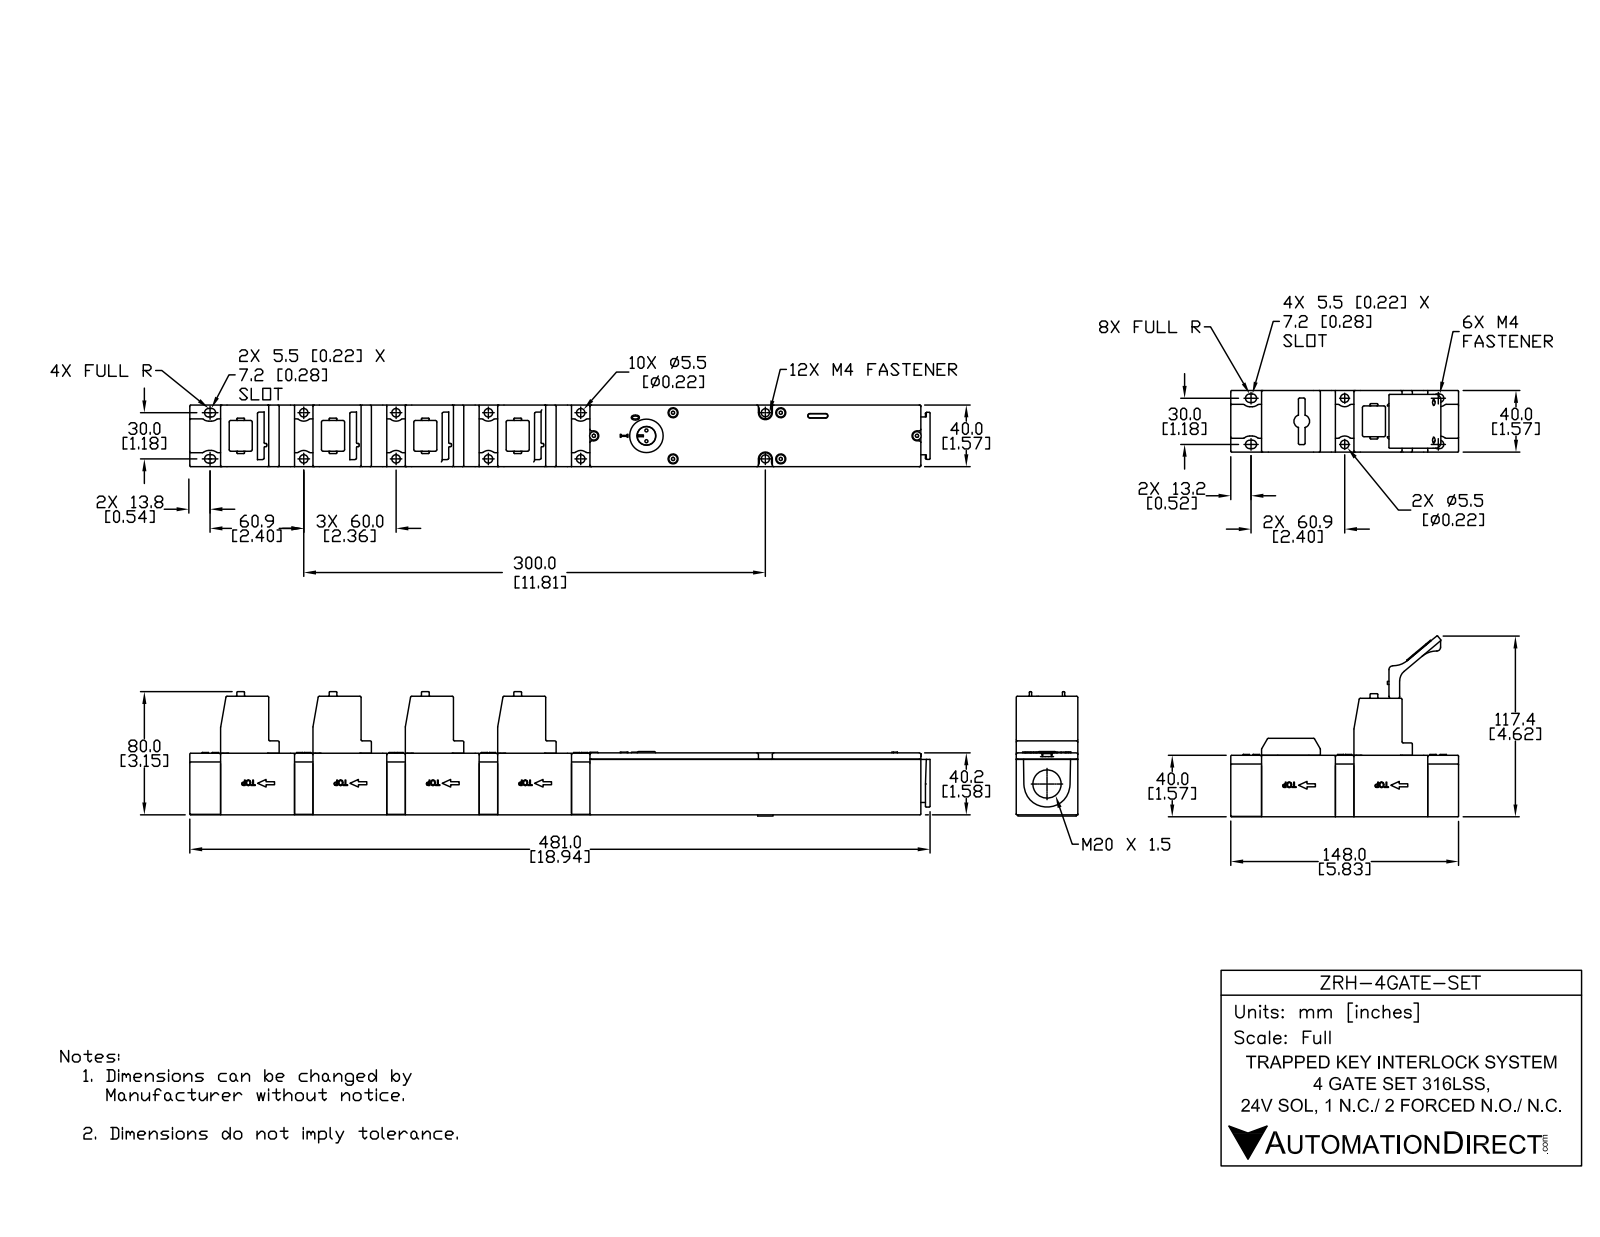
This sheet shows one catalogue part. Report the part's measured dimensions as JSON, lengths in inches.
{"part_name": "ST2323_STS-Schluessel_mit_Kodierung_NEU; ST2110_B; ST2130_01; ST2330_Bajonett (+4 more)", "step_written_by": "SolidWorks 2017 (AUTOMOTIVE_DESIGN)", "units": "inches", "bodies": {"solids": 44, "faces": 17763, "planar": 7815, "cylindrical": 2190, "other": 7758}, "overall_size": [19.525, 18.937, 4.641], "volume_in3": 127.8, "surface_area_in2": 595, "round_holes": [[0.157, 24], [0.217, 16], [0.097, 12], [0.079, 10], [0.13, 6], [0.097, 4], [0.256, 4], [0.236, 3], [0.209, 2], [0.079, 1], [0.134, 1], [0.374, 1]], "round_bosses_or_shafts": [[0.217, 6], [0.118, 6], [0.394, 5], [0.472, 1], [0.276, 1], [0.228, 1], [0.161, 1]], "partial_cylinders_radius": [[0.02, 654], [0.039, 267], [0.03, 207], [0.018, 114], [0.217, 52], [0.006, 46], [0.079, 37], [0.108, 36]], "face_to_face_distances": [1.575, 2.362, 1.89, 0.472, 4.252, 4.724, 13.11, 8.386, 10.748, 8.656], "hole_center_spacings": [2.362, 1.181, 0.571, 2.641, 8.656, 4.363, 2.43, 4.293]}
